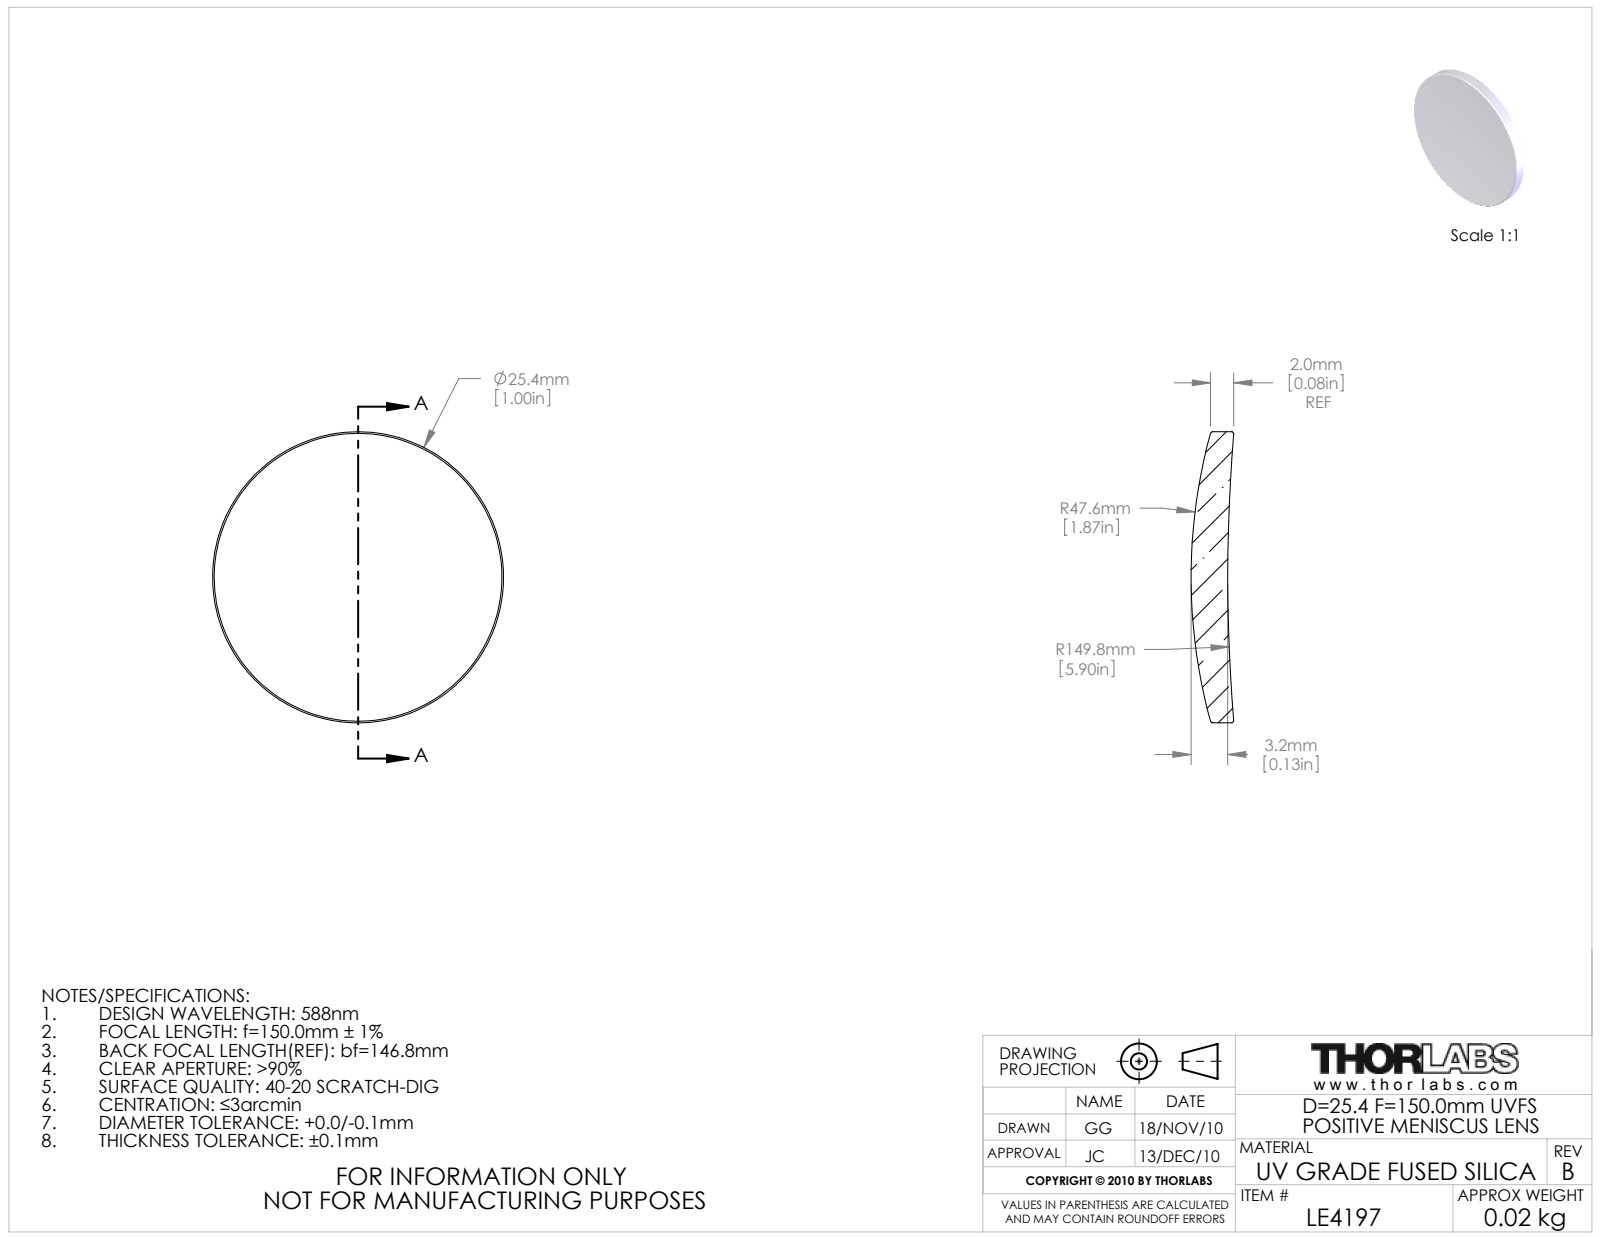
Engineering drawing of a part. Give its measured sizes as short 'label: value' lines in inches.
name: 4206-E0W
written by: SolidWorks 2009 (AUTOMOTIVE_DESIGN)
unit: in
bodies: 1 solid, 10 faces (0 planar, 2 cylindrical, 8 other)
size: 1 × 1 × 0.147
volume: 0.081 in³; area: 1.818 in²
bosses: 1× ⌀1
